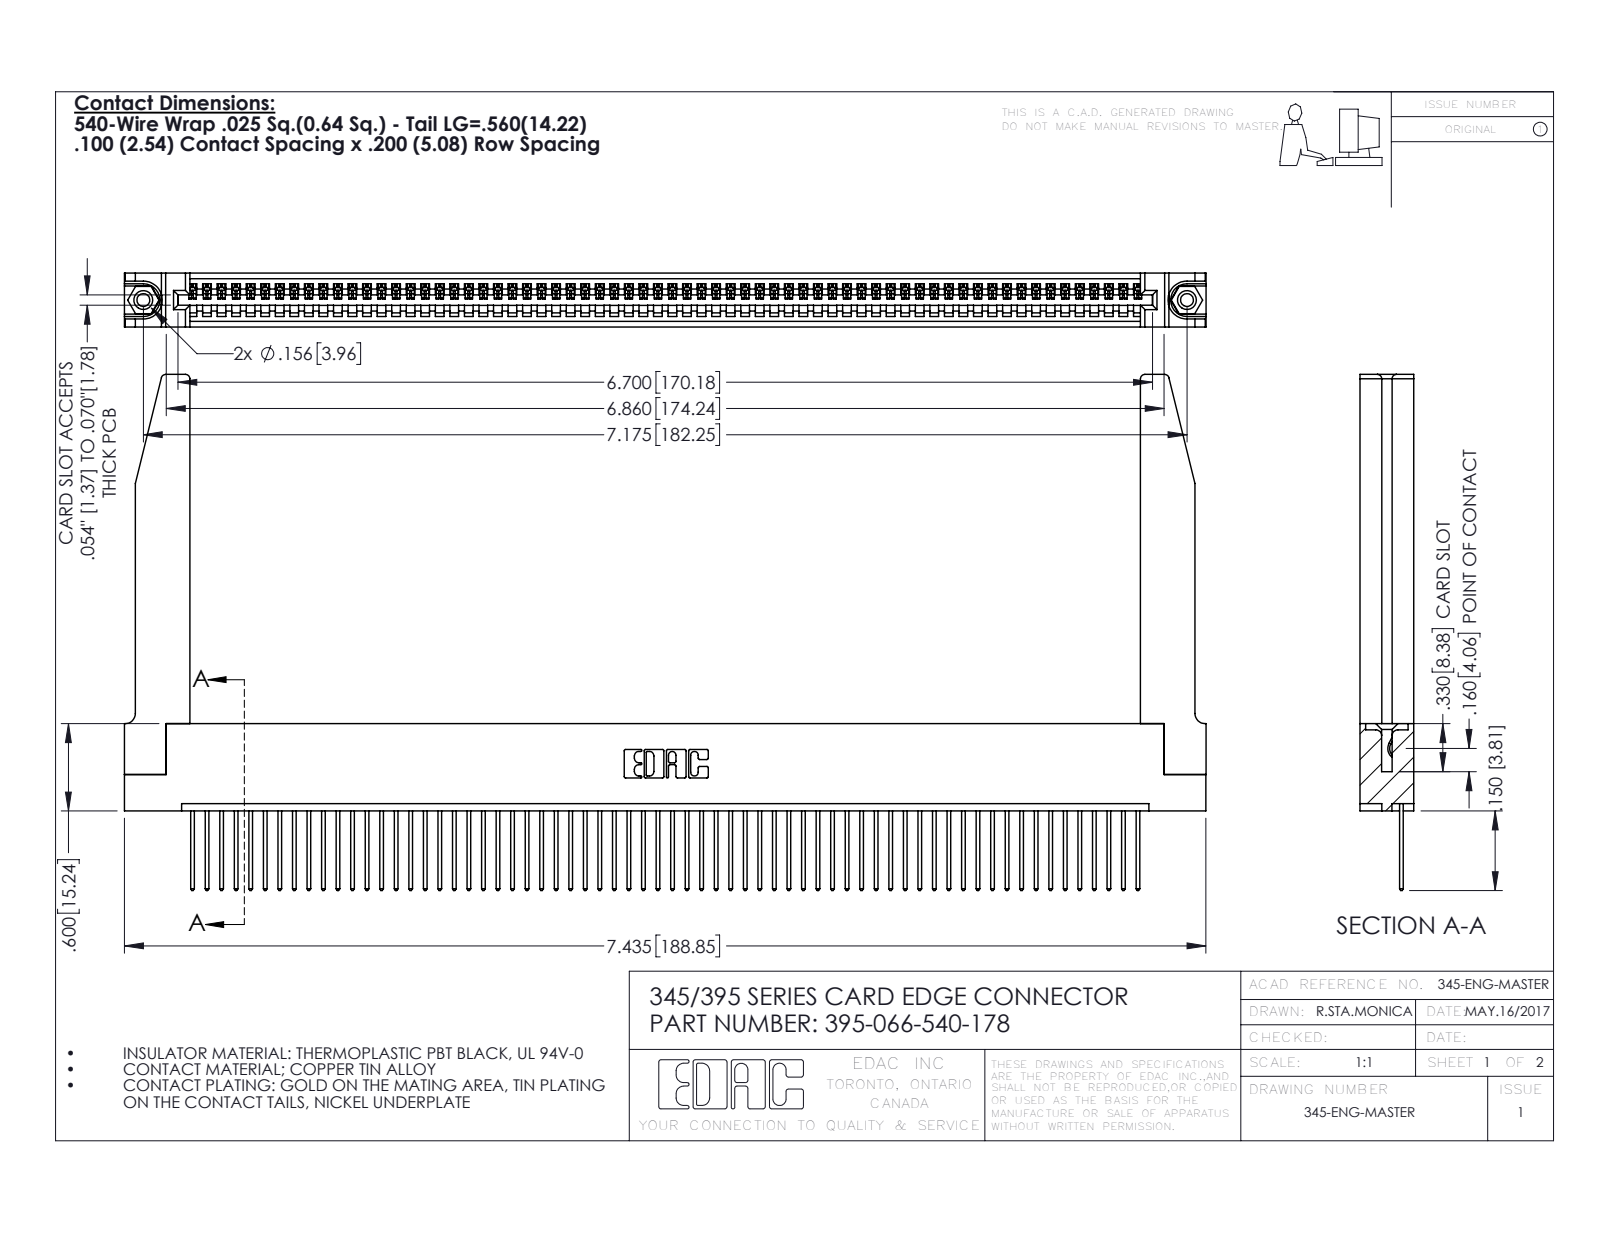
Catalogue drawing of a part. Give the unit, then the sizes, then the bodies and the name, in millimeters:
Units: millimetres
Overall size (bounding box): 188.9 × 90.1 × 9.4
Round holes (diameter × count): ⌀2.3 ×2, ⌀3.2 ×2, ⌀4 ×2, ⌀1.6 ×1
Round bosses / shafts (diameter × count): ⌀3.9 ×2
Partial cylindrical surfaces — rounded edges, fillets, slot ends (radius × count): R0.2 ×132, R0.3 ×132, R0.3 ×22, R0.8 ×8, R0.2 ×6, R0.8 ×6, R0.7 ×3, R0.8 ×2
Main face-to-face distances: 1.8, 7.6, 9.4, 2.5, 6.9, 0.6, 5.1, 5.7, 3.8, 3.8
Hole centre spacings: 6.9, 176.3, 182.2
Volume: 25 990 mm³ · Surface area: 32 030 mm²
Bodies: 71 solids, 4188 faces (2862 planar, 1274 cylindrical, 52 other)
Part name (STEP PRODUCT): 345-292-001_345-293-140; 395-066-540-178; 345 Part_Flush Mounting Lugs - 0.156 Dia-TH; 345-220-078_345-220-078 (+1 more)
STEP written by: SolidWorks 2016 (CONFIG_CONTROL_DESIGN)
